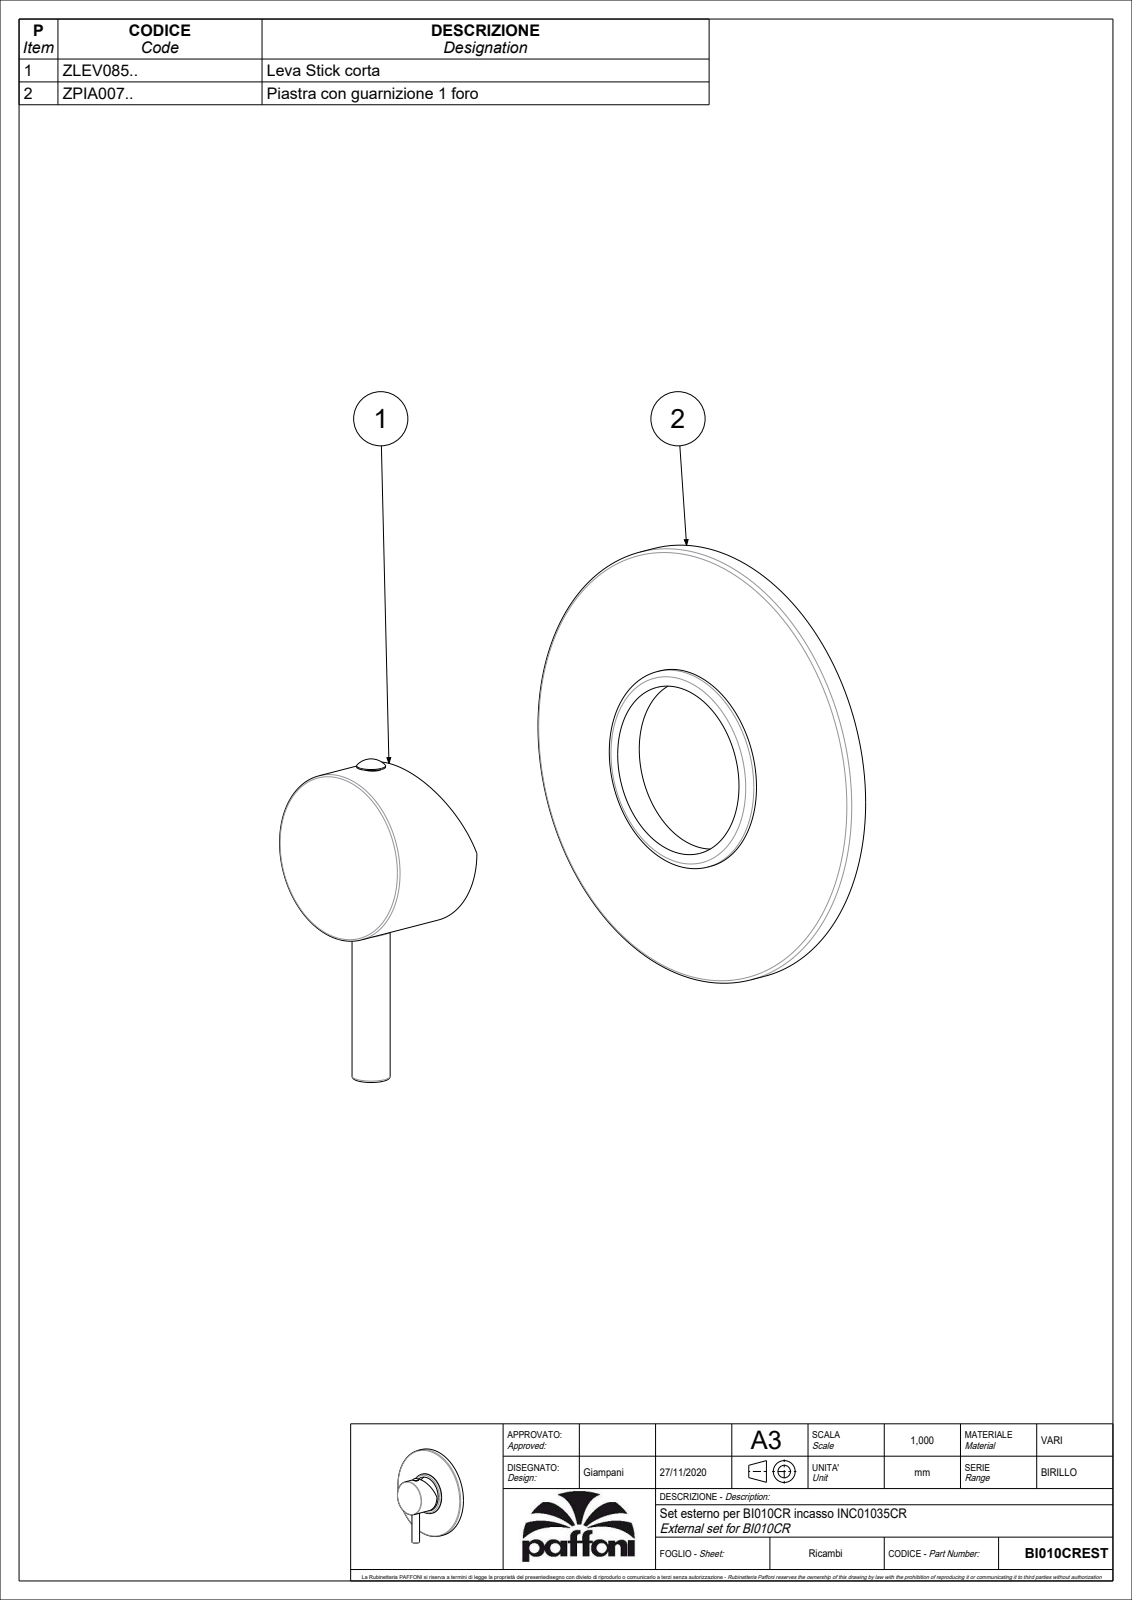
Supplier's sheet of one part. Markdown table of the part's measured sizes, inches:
| quantity | value |
| --- | --- |
| part name | BI010CREST |
| STEP written by | CREO PARAMETRIC BY PTC INC, 2020044 (CONFIG_CONTROL_DESIGN) |
| units | inches |
| bodies | 2 solids, 191 faces (48 planar, 54 cylindrical, 89 other) |
| overall size | 4.724 × 4.567 × 1.689 |
| volume | 1.672 in³ |
| surface area | 57.6 in² |
| round holes (diameter × count) | 0.118 × 1, 1.772 × 1, 1.969 × 1, 4.488 × 1 |
| round bosses / shafts (diameter × count) | 4.567 × 1, 2.087 × 1, 1.752 × 1, 0.394 × 1, 0.299 × 1, 0.217 × 1, 0.197 × 1 |
| partial cylindrical surfaces (radius × count) | 0.02 × 8 |
| main face-to-face distances | 0.157, 1.063, 0.453, 1.516, 0.098, 0.315, 0.354, 1.161, 0.059, 0.138 |
